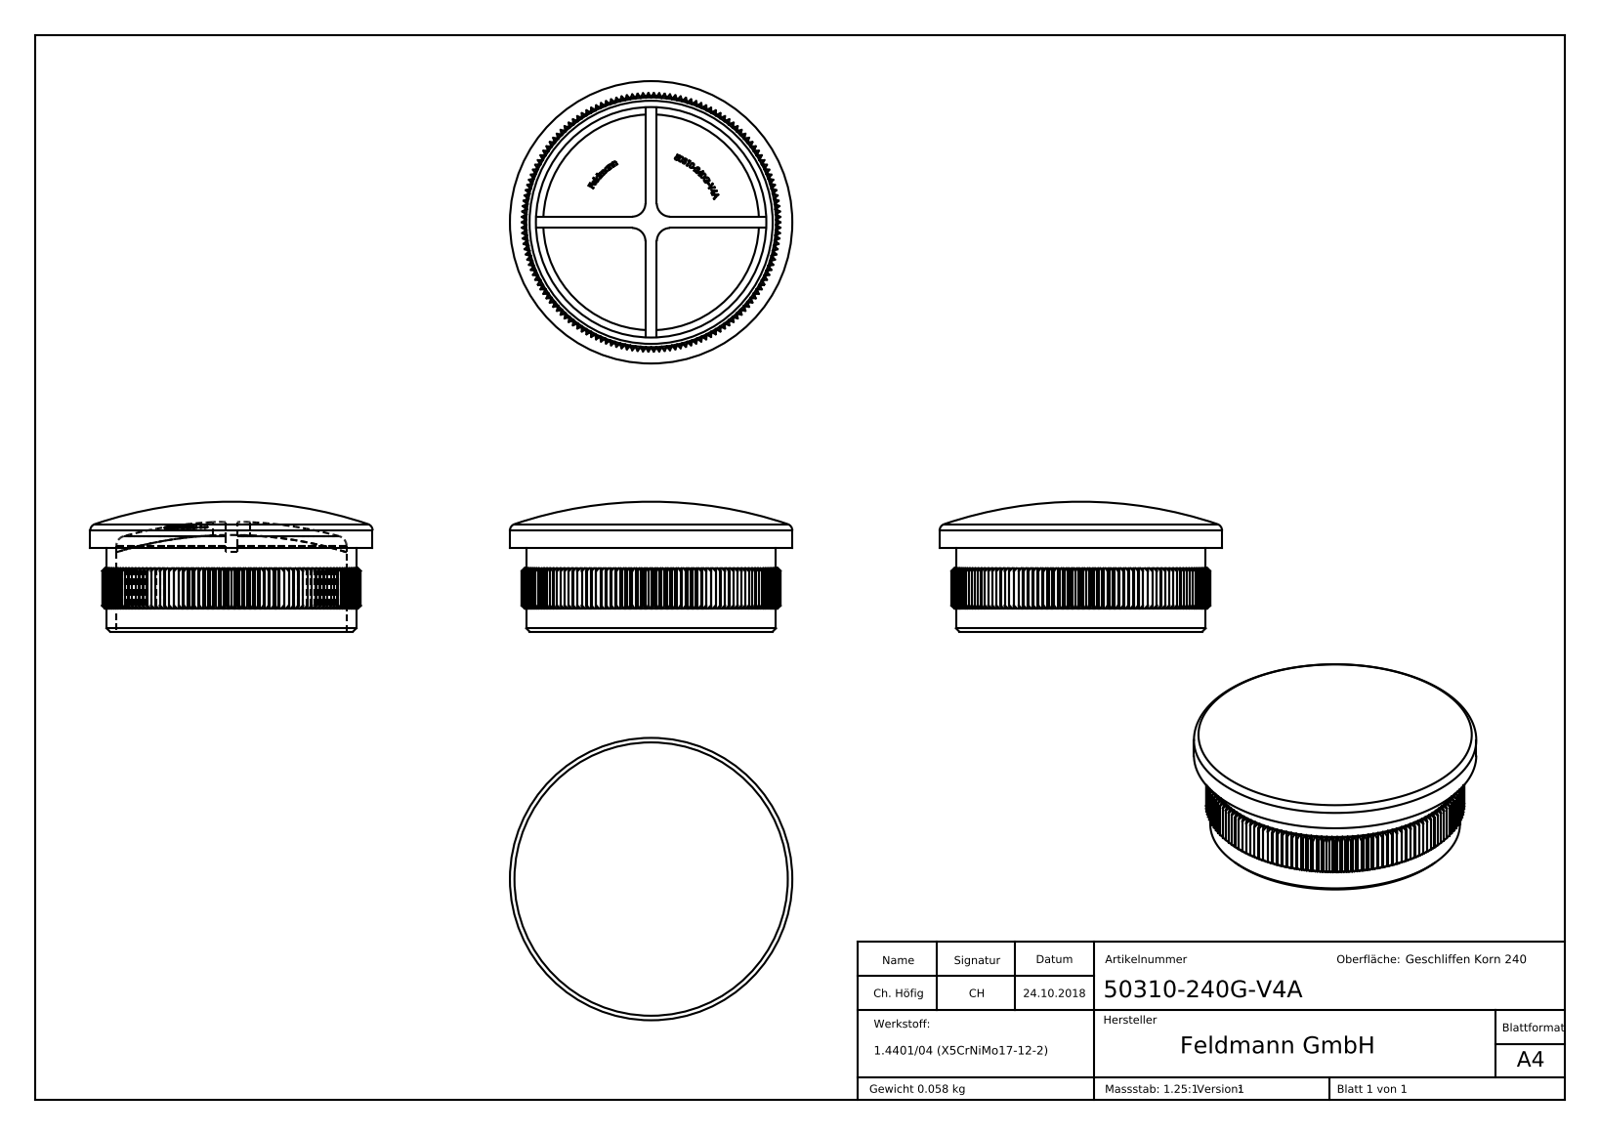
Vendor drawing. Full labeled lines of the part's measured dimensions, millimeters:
Part name (STEP PRODUCT): 50310-240G-V4A
STEP written by: SolidWorks 2015 (CONFIG_CONTROL_DESIGN)
Units: millimetres
Bodies: 1 solid, 1358 faces (747 planar, 162 cylindrical, 449 other)
Overall size (bounding box): 42.4 × 42.4 × 19.5
Volume: 7 304 mm³ · Surface area: 7 220 mm²
Round holes (diameter × count): ⌀34.6 ×1
Round bosses / shafts (diameter × count): ⌀42.4 ×1, ⌀37.5 ×1
Partial cylindrical surfaces — rounded edges, fillets, slot ends (radius × count): R2 ×4, R19.4 ×1
Main face-to-face distances: 18.75, 18.76, 18.74, 1.7, 12.5, 18.78, 3.5, 9, 9.5, 6
